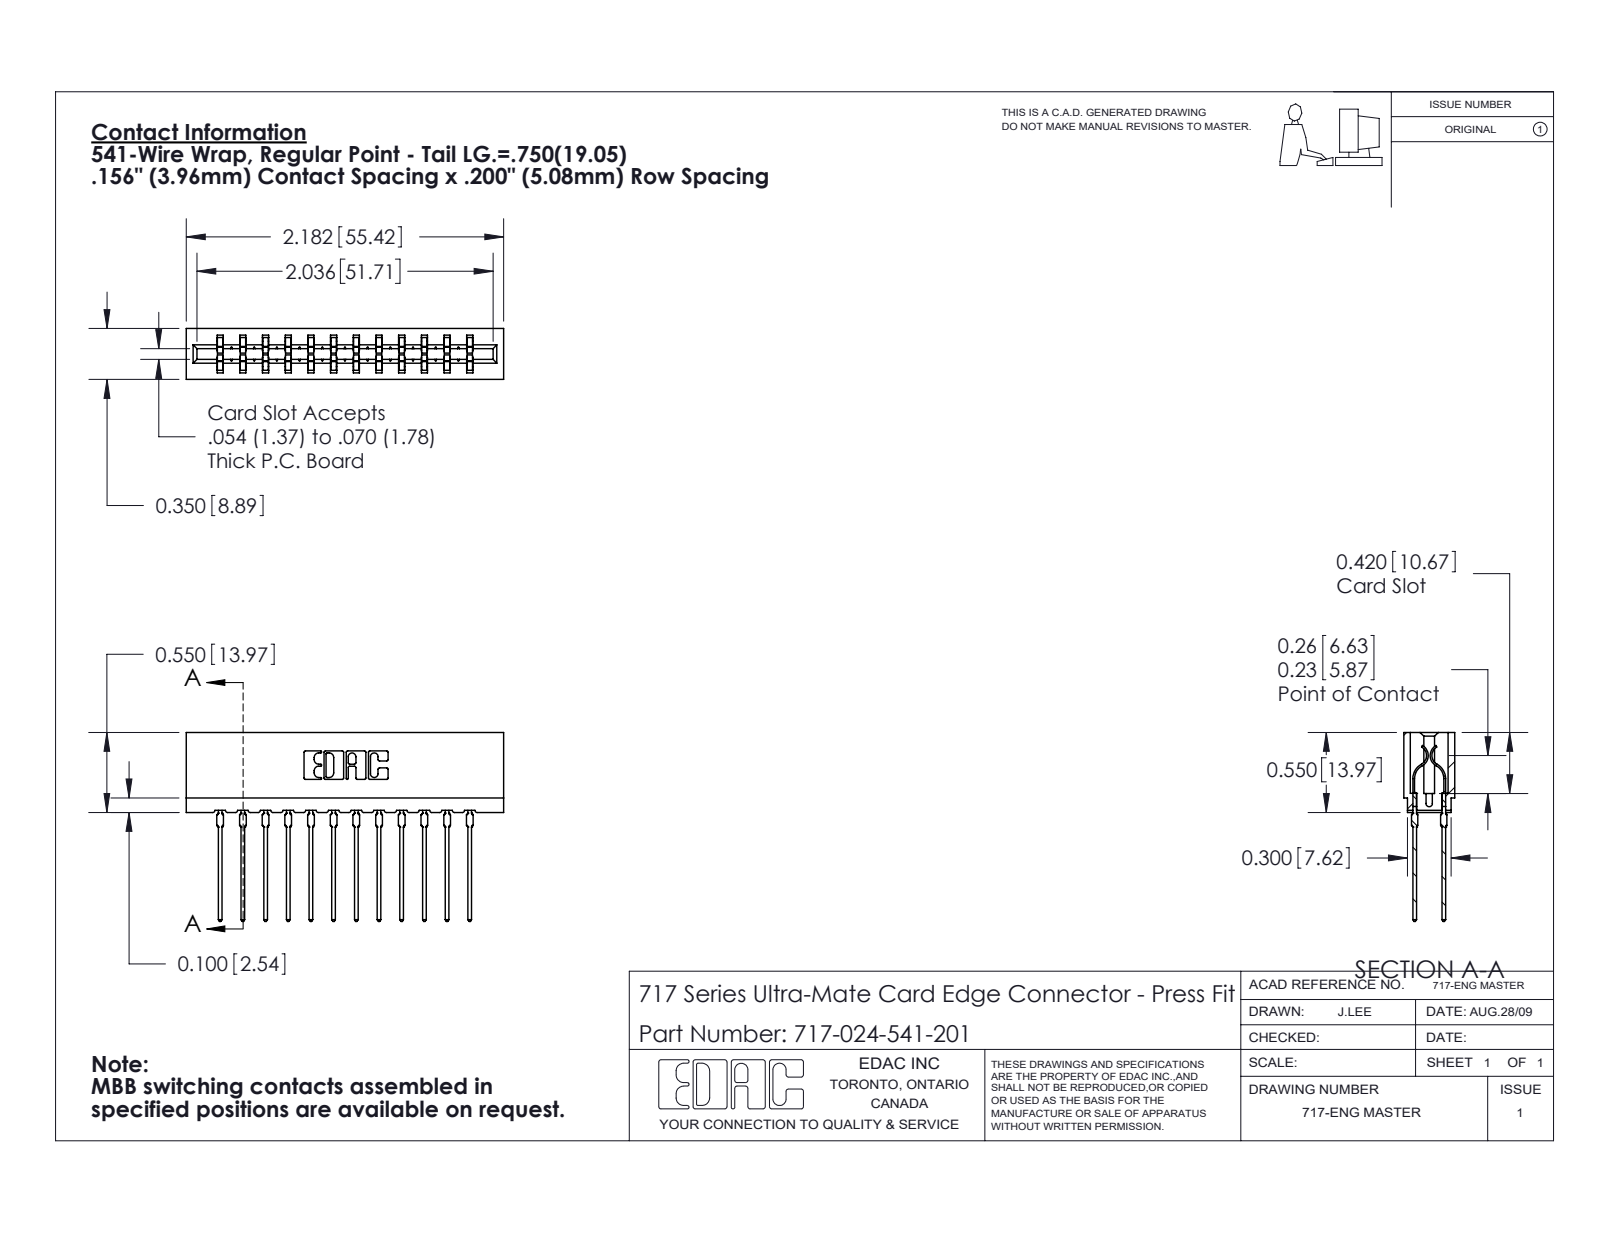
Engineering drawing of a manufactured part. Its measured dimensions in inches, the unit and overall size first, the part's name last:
Units: inches
Overall size (bounding box): 2.182 × 1.299 × 0.35
Partial cylindrical surfaces — rounded edges, fillets, slot ends (radius × count): R0.021 ×48, R0.015 ×24, R0.01 ×22, R0.005 ×8, R0.011 ×8, R0.007 ×6, R0.031 ×6, R0.026 ×3
Main face-to-face distances: 0.212, 0.138, 0.156, 0.624, 0.35, 0.063, 0.287, 0.076, 0.149, 0.468
Volume: 0.308 in³ · Surface area: 12.16 in²
Bodies: 25 solids, 2254 faces (1170 planar, 460 cylindrical, 624 other)
Part name (STEP PRODUCT): 717 Part_Insulator Option - 06; 717-024-541-201; 745-292-001_541
STEP written by: SolidWorks 2020 (CONFIG_CONTROL_DESIGN)
